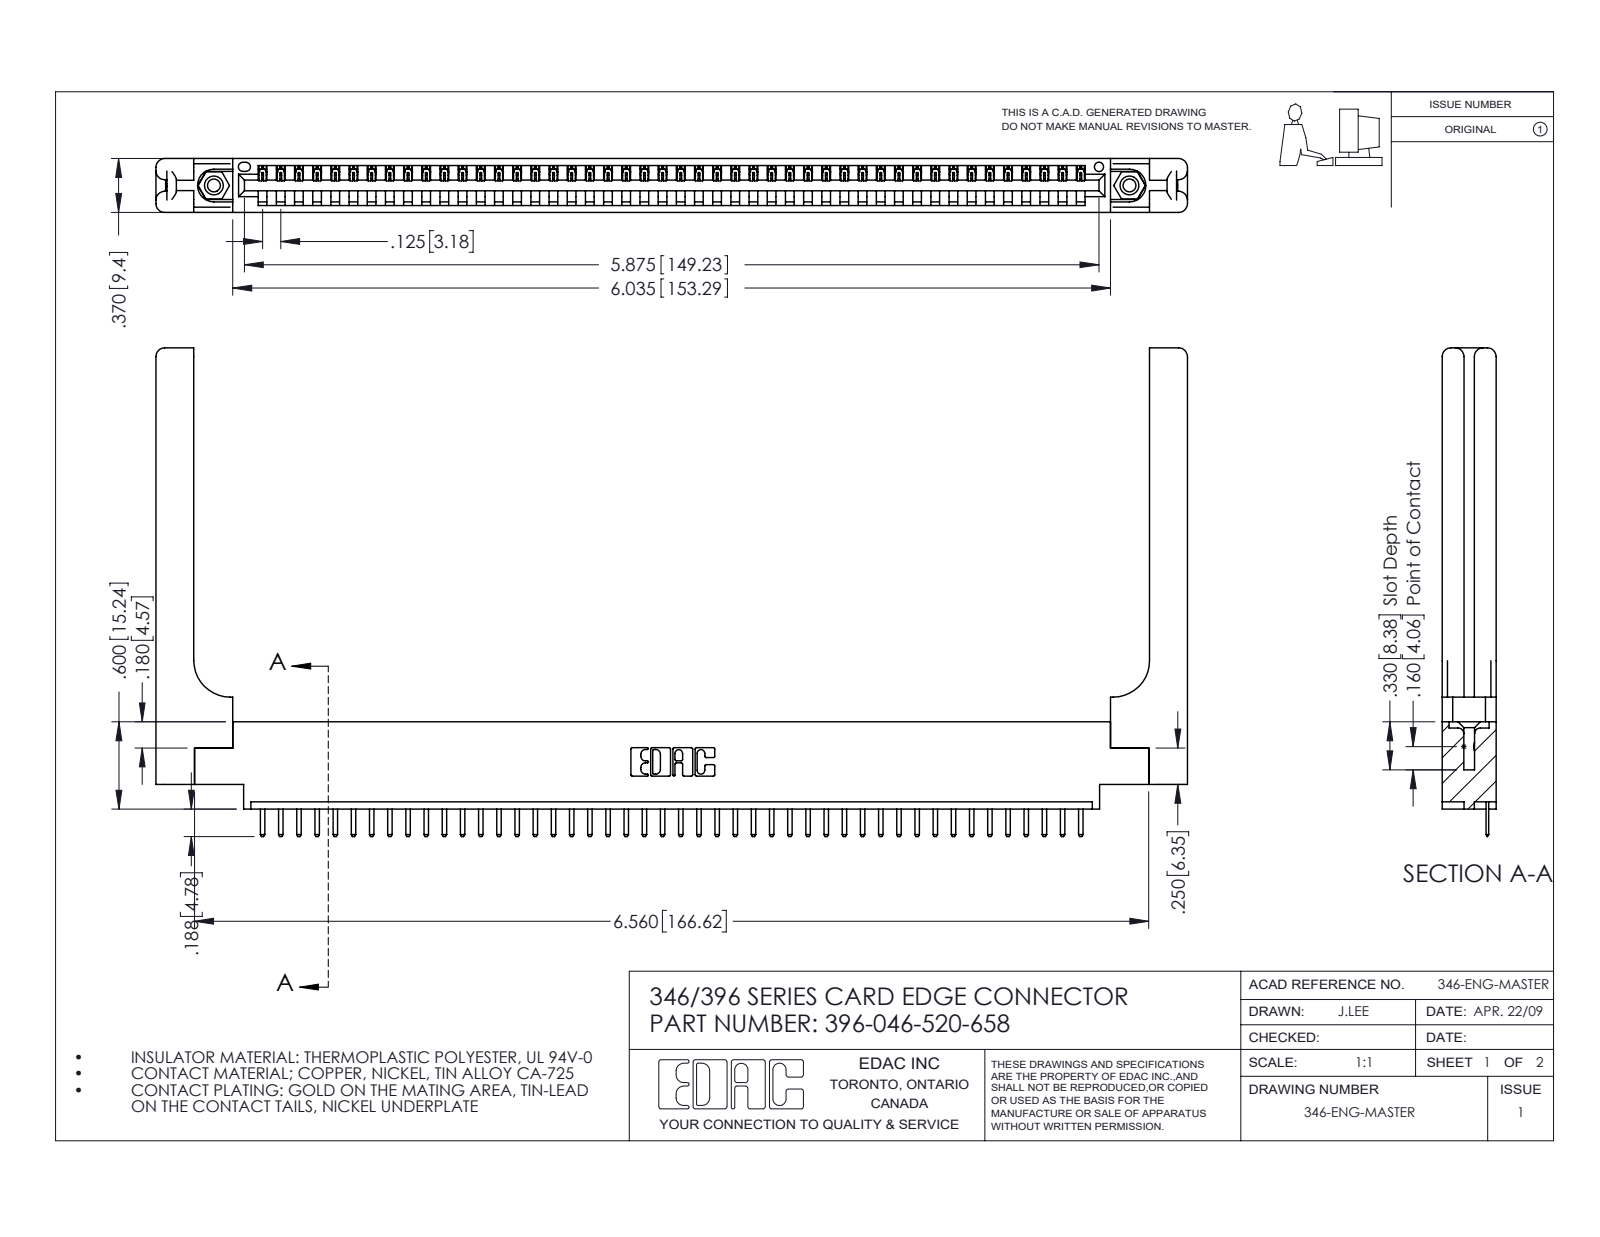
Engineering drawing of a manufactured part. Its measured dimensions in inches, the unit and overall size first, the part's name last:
Units: inches
Overall size (bounding box): 7.091 × 3.358 × 0.37
Round holes (diameter × count): ⌀0.089 ×2, ⌀0.125 ×2, ⌀0.156 ×2, ⌀0.064 ×1
Round bosses / shafts (diameter × count): ⌀0.155 ×2
Partial cylindrical surfaces — rounded edges, fillets, slot ends (radius × count): R0.01 ×94, R0.006 ×92, R0.01 ×22, R0.06 ×16, R0.007 ×6, R0.031 ×6, R0.026 ×3, R0.03 ×2
Main face-to-face distances: 0.37, 0.048, 0.322, 0.072, 0.148, 0.15, 0.25, 0.298, 0.025, 0.222
Hole centre spacings: 0.246, 6.086, 6.295
Volume: 1.495 in³ · Surface area: 40.54 in²
Bodies: 51 solids, 3234 faces (2160 planar, 1014 cylindrical, 60 other)
Part name (STEP PRODUCT): 345-292-001_345-293-120; 396-046-520-658; 346 Part_0.170 Offset - 0.156 Dia-TH; 345-250-001_345-250-001-102 (+1 more)
STEP written by: SolidWorks 2016 (CONFIG_CONTROL_DESIGN)
